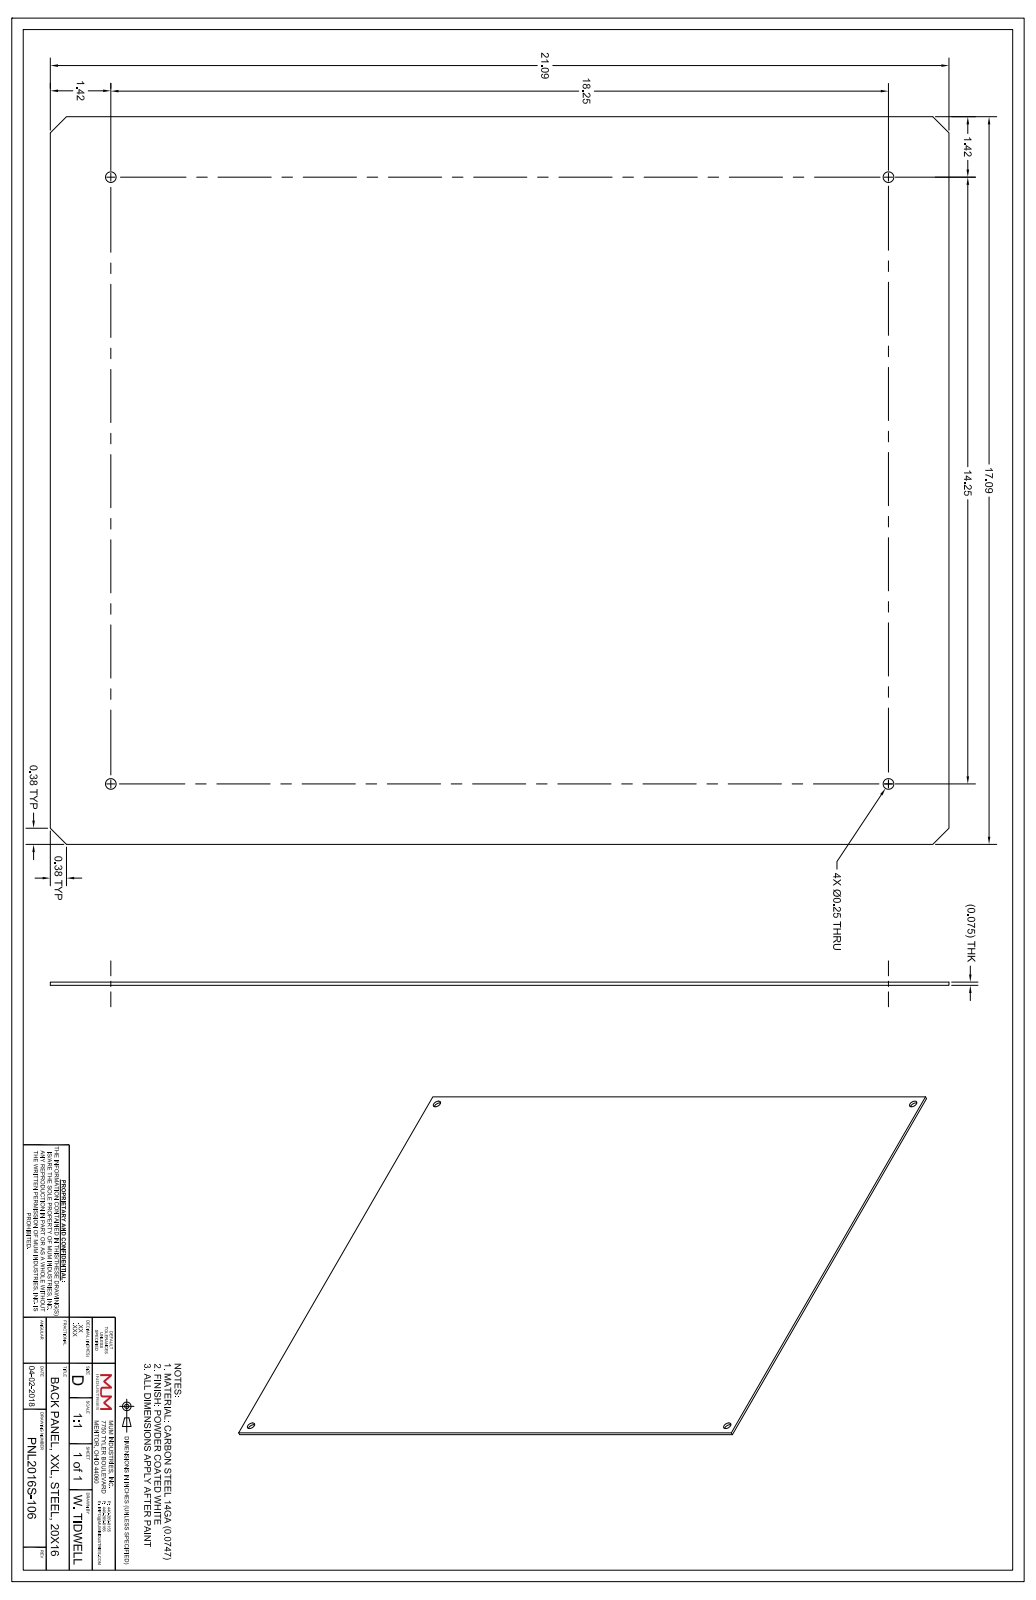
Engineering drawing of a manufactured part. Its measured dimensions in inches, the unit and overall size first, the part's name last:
Units: inches
Overall size (bounding box): 21.09 × 17.09 × 0.075
Round holes (diameter × count): ⌀0.25 ×4
Main face-to-face distances: 0.075, 17.09, 21.09, 26.463
Hole centre spacings: 14.25, 18.25, 23.154
Volume: 26.89 in³ · Surface area: 725.8 in²
Bodies: 1 solid, 14 faces (10 planar, 4 cylindrical, 0 other)
Part name (STEP PRODUCT): SBP-2016-XXL-P10
STEP written by: SolidWorks 2018 (AUTOMOTIVE_DESIGN)
